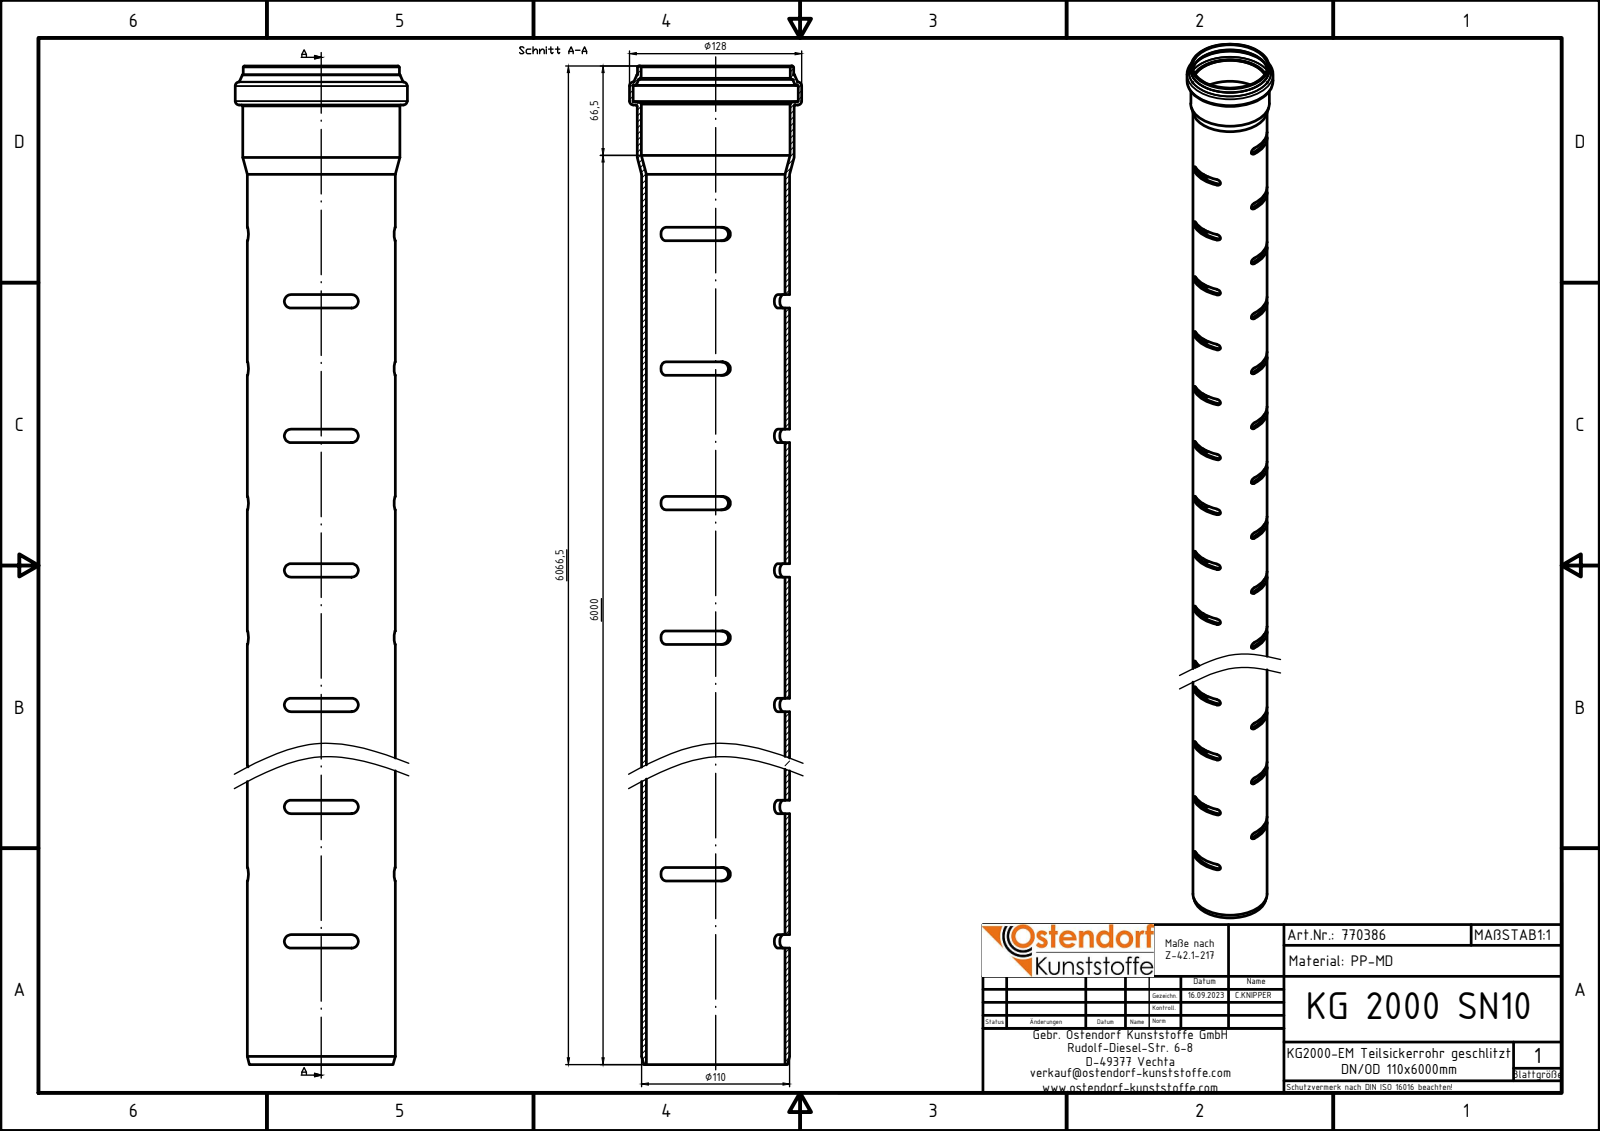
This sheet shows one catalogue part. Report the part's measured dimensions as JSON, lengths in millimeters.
{"part_name": "770386z", "step_written_by": "Autodesk Inventor 2024 (AUTOMOTIVE_DESIGN)", "units": "millimeters", "bodies": {"solids": 1, "faces": 744, "planar": 359, "cylindrical": 363, "other": 22}, "overall_size": [6066.5, 128, 128], "volume_mm3": 6797000, "surface_area_mm2": 3955000, "round_holes": [[102.96, 1], [110.5, 1], [110.9, 1], [122.8, 1]], "round_bosses_or_shafts": [[128, 1], [116.7, 1], [116.1, 1], [110, 1]], "partial_cylinders_radius": [[5, 354]], "face_to_face_distances": [100, 200, 300, 400, 10, 110, 500, 90, 210, 190]}
